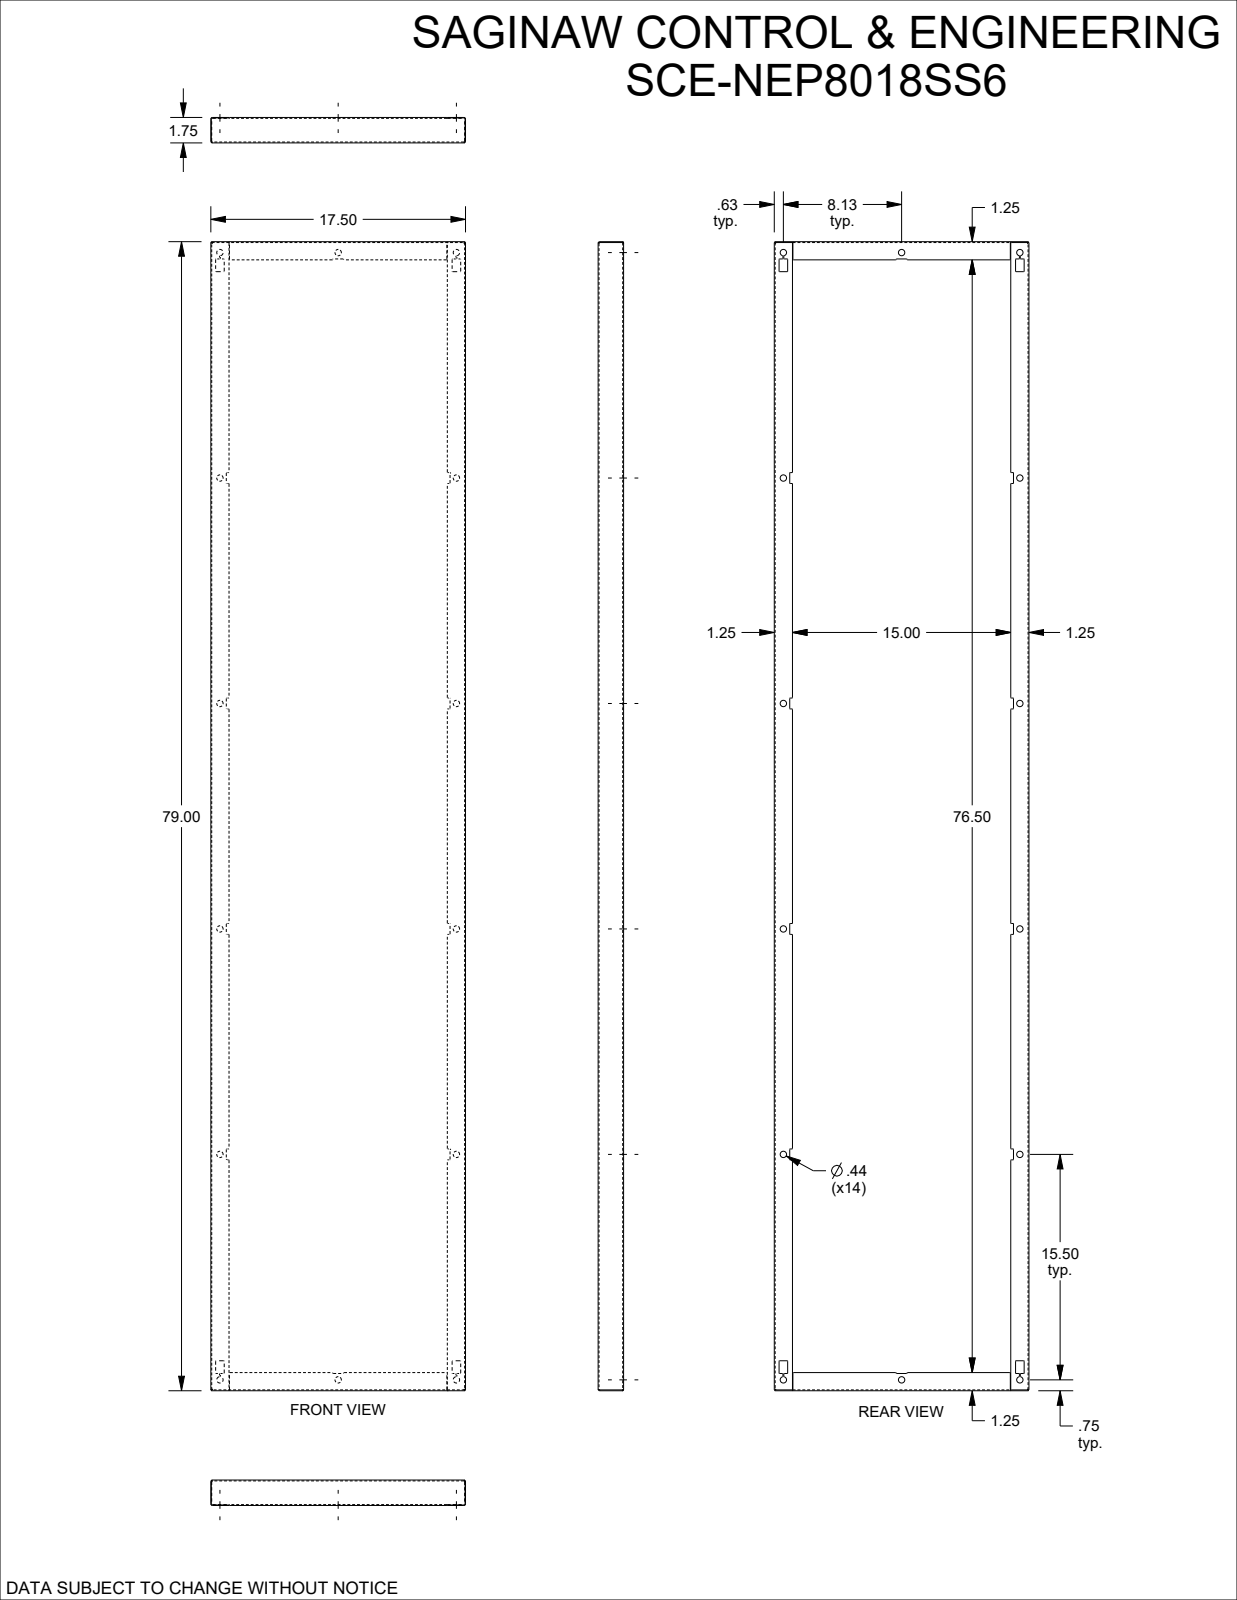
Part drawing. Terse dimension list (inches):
name: SCE-NEP8018
written by: SolidWorks 2023 (AUTOMOTIVE_DESIGN)
unit: in
bodies: 1 solid, 166 faces (80 planar, 78 cylindrical, 8 other)
size: 79 × 17.5 × 1.75
volume: 115.3 in³; area: 3 866 in²
holes: 14× ⌀0.437
rounds: 64× R0.03
face distances: 0.06, 1.69, 17.44, 1.75, 1.63, 17.5, 17.38, 78.94, 79, 78.88
hole spacings: 15.5, 22.457, 31, 35.001, 16.25, 46.5, 49.258, 8.125
